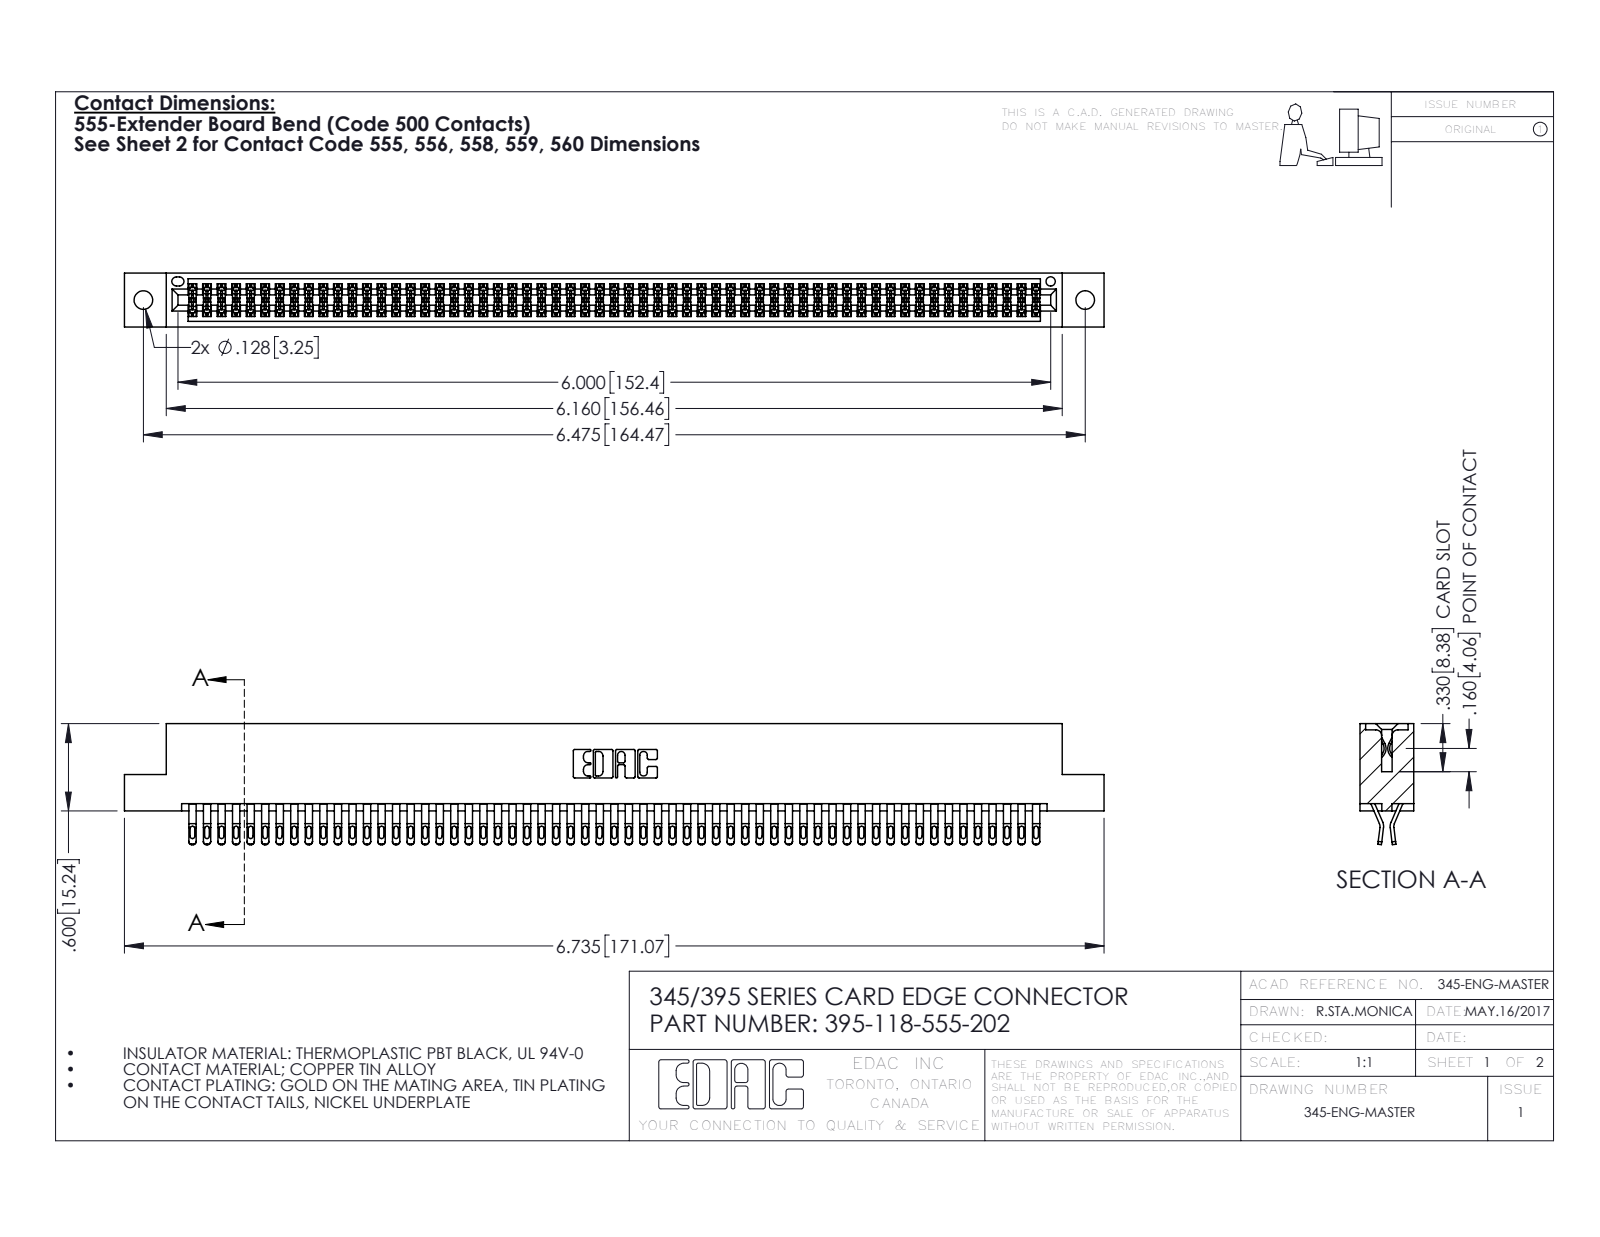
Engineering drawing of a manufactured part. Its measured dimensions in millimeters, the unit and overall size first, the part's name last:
Units: millimetres
Overall size (bounding box): 171.1 × 21.1 × 9.4
Round holes (diameter × count): ⌀3.3 ×2, ⌀1.6 ×1
Partial cylindrical surfaces — rounded edges, fillets, slot ends (radius × count): R0.4 ×295, R0.5 ×236, R0.2 ×177, R0.3 ×22, R0.2 ×6, R0.8 ×6, R0.7 ×3, R0.3 ×2
Main face-to-face distances: 7.6, 1.8, 0.6, 9.4, 5.1, 2.5, 6.9, 5.7, 4.4, 3.8
Hole centre spacings: 6.9, 158.5, 164.5
Volume: 17 080 mm³ · Surface area: 26 500 mm²
Bodies: 119 solids, 6734 faces (3738 planar, 2996 cylindrical, 0 other)
Part name (STEP PRODUCT): 395-118-555-202; 345 Part_Flush Mounting Lugs - 0.128 Dia; 345-292-001_555 Tail
STEP written by: SolidWorks 2016 (CONFIG_CONTROL_DESIGN)
